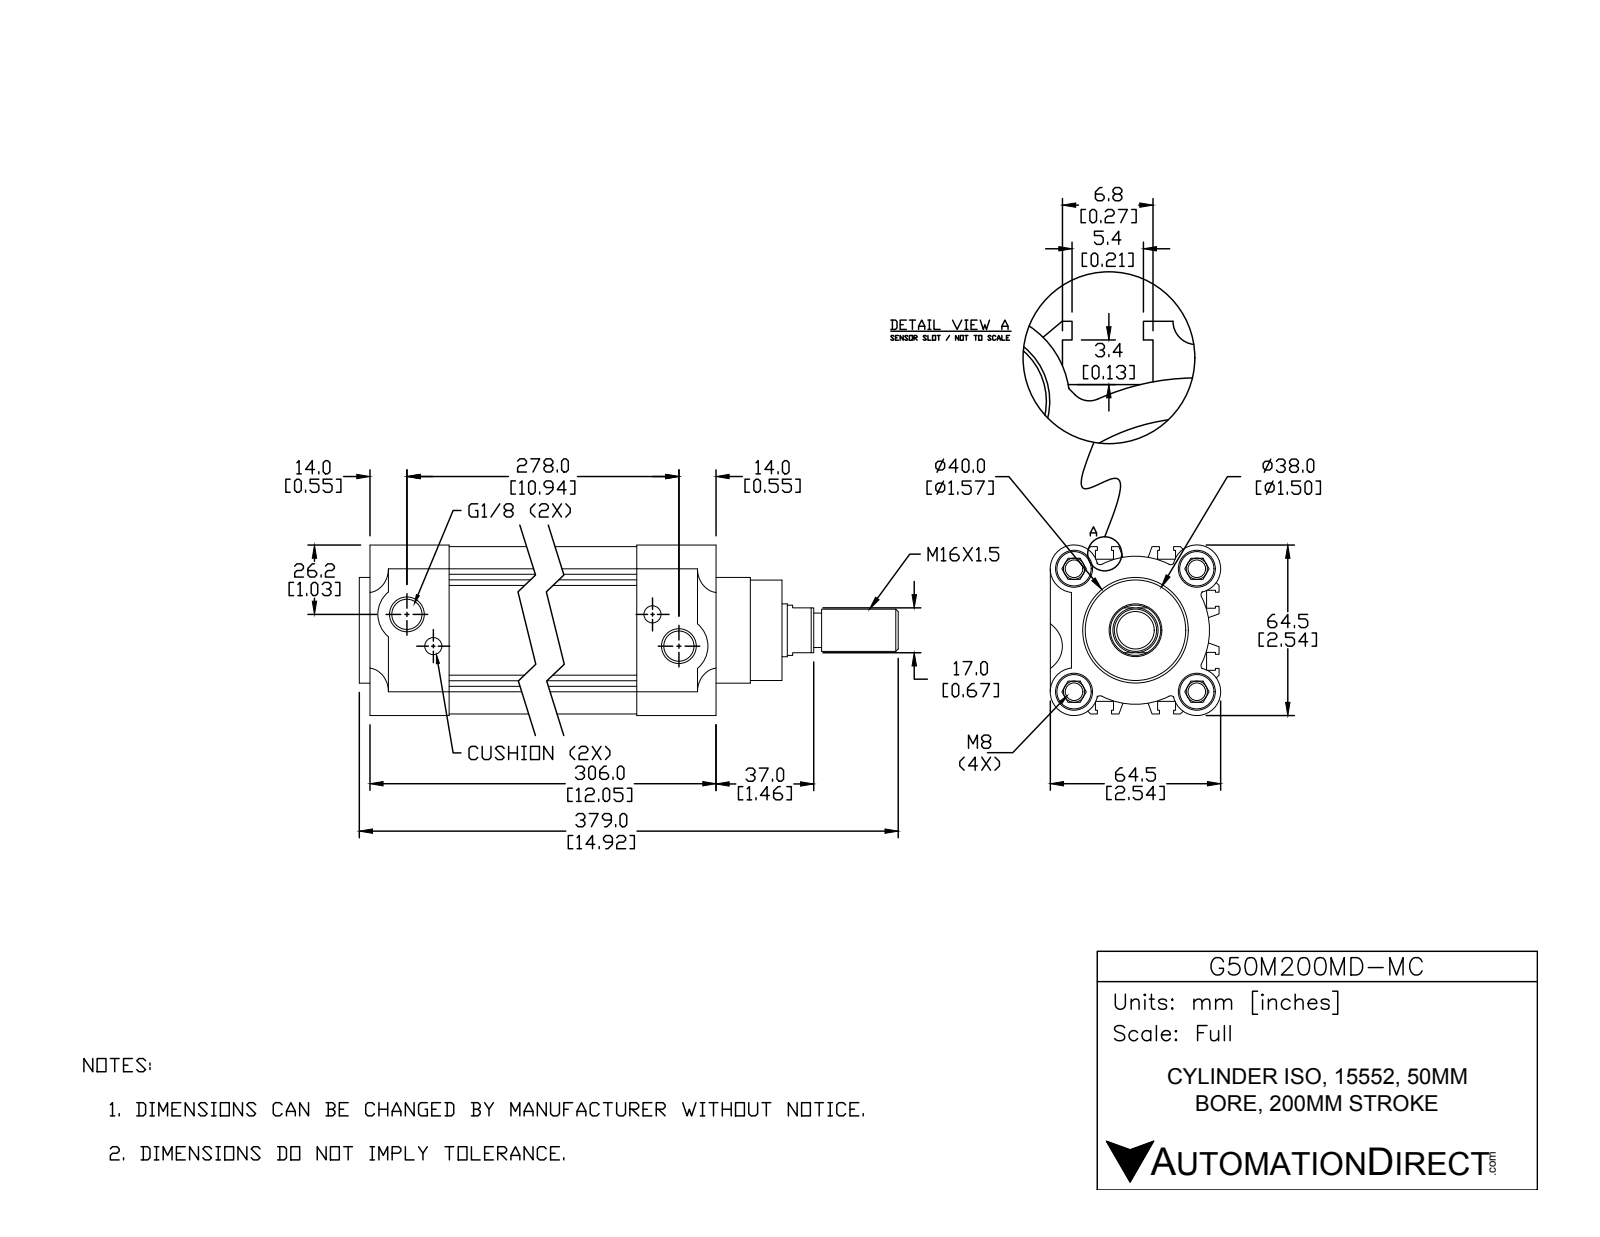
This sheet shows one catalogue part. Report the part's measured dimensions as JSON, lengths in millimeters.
{"part_name": "50-HL; 50-200-90.5-B; 50121200-R; G50M200MD-MC (+1 more)", "step_written_by": "SolidWorks 2015 (CONFIG_CONTROL_DESIGN)", "units": "millimeters", "bodies": {"solids": 4, "faces": 418, "planar": 236, "cylindrical": 138, "other": 44}, "overall_size": [379, 64.5, 64.5], "volume_mm3": 794000, "surface_area_mm2": 213600, "round_holes": [[6.7, 4], [14, 4], [6.5, 2], [6.7, 2], [11.5, 2], [20, 1]], "round_bosses_or_shafts": [[13, 5], [50, 1], [40, 1], [38, 1], [19, 1], [16, 1]], "partial_cylinders_radius": [[1.5, 12], [0.1, 6], [8.4, 4], [9, 4], [11, 2], [27.5, 1], [28, 1]], "face_to_face_distances": [4.7, 58.5, 63.3, 27, 41.8, 23.5, 40, 16.5, 23.3, 46.8], "hole_center_spacings": [32.9, 46.5, 15.6, 65.8, 268, 258.3, 278.3]}
